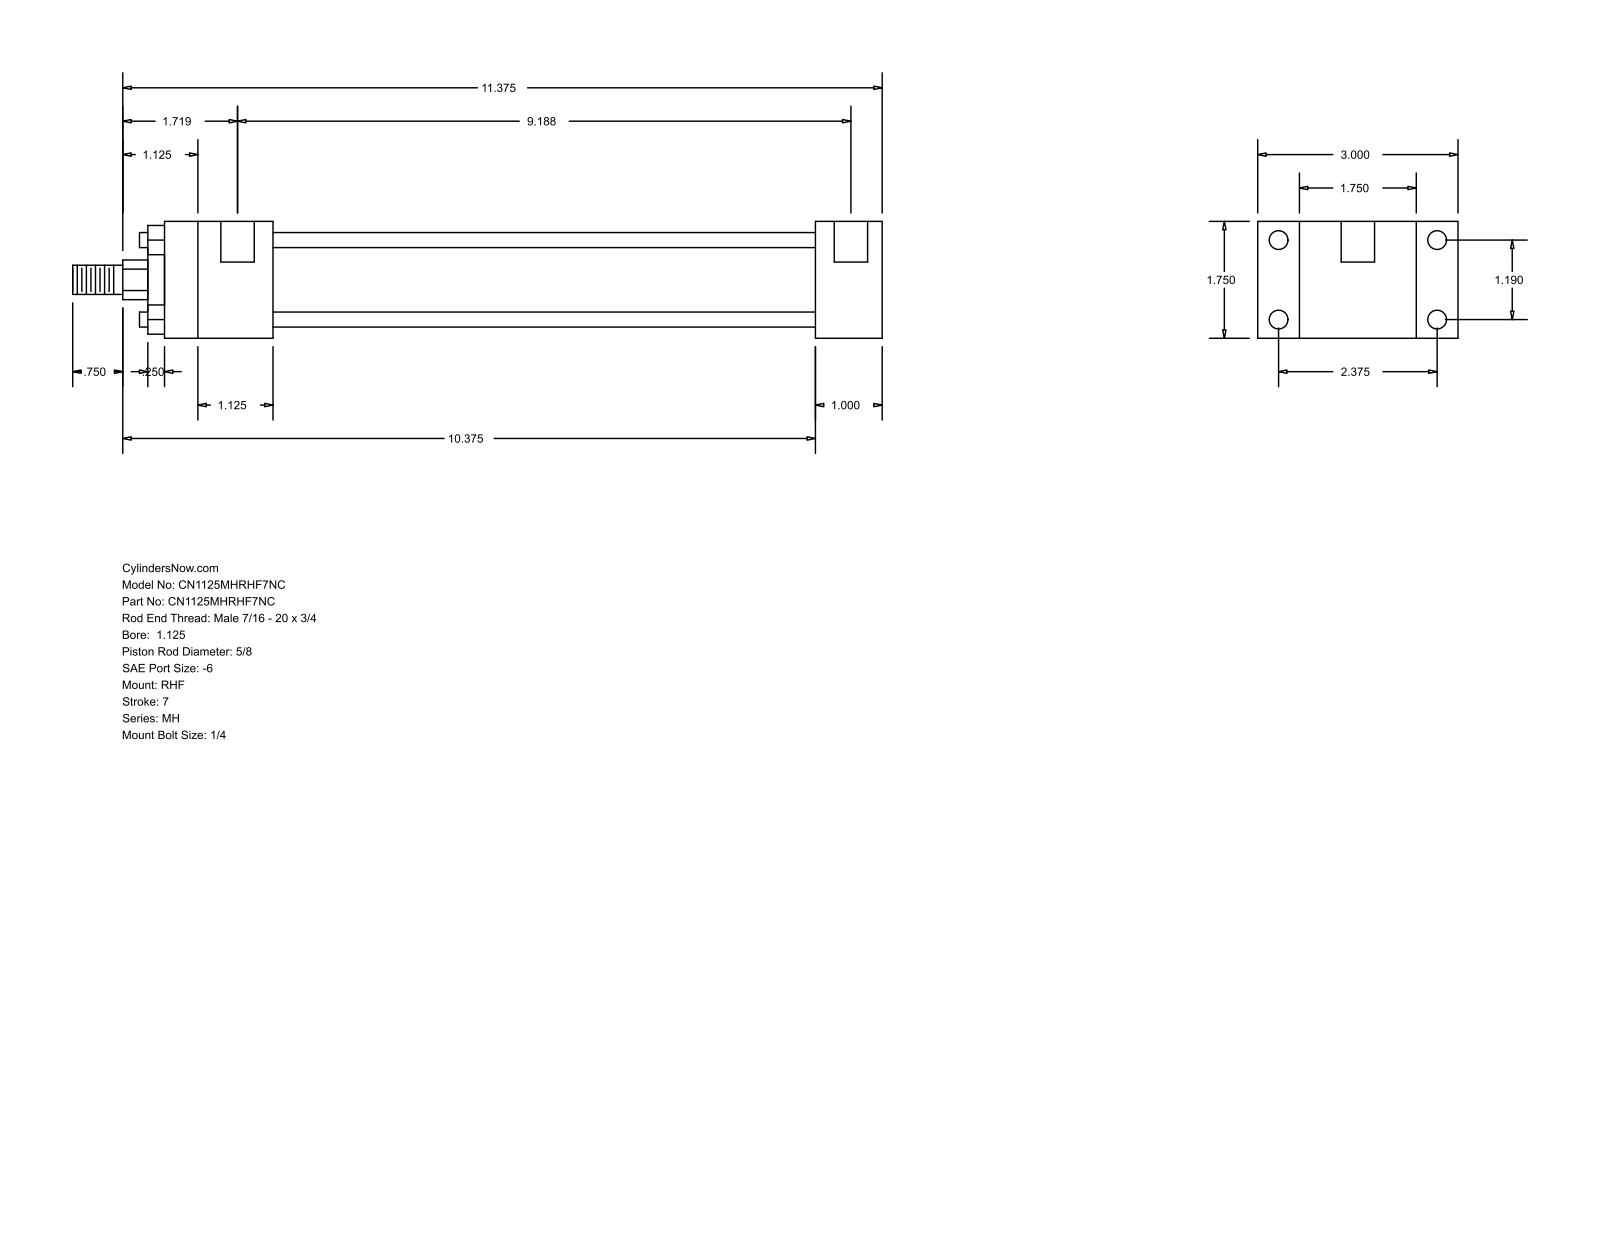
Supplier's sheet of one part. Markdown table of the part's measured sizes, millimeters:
| quantity | value |
| --- | --- |
| part name | MH_RHF__0112_0.625 |
| STEP written by | GSSL Pune (CONFIG_CONTROL_DESIGN) |
| units | millimeters |
| bodies | 0 solids, 88 faces (60 planar, 28 cylindrical, 0 other) |
| overall size | 307.98 × 76.2 × 44.45 |
| round holes (diameter × count) | 5.56 × 4, 7.14 × 4, 12.7 × 2 |
| round bosses / shafts (diameter × count) | 5.71 × 4, 34.92 × 1, 28.57 × 1, 15.88 × 1, 11.11 × 1 |
| partial cylindrical surfaces (radius × count) | 7.54 × 1 |
| main face-to-face distances | 44.46, 15.87, 60.33, 25.41, 76.2, 206.37, 231.78, 41.27, 247.64, 273.05 |
| hole center spacings | 30.22, 60.32, 67.47, 230.19, 3.17, 233.36 |
